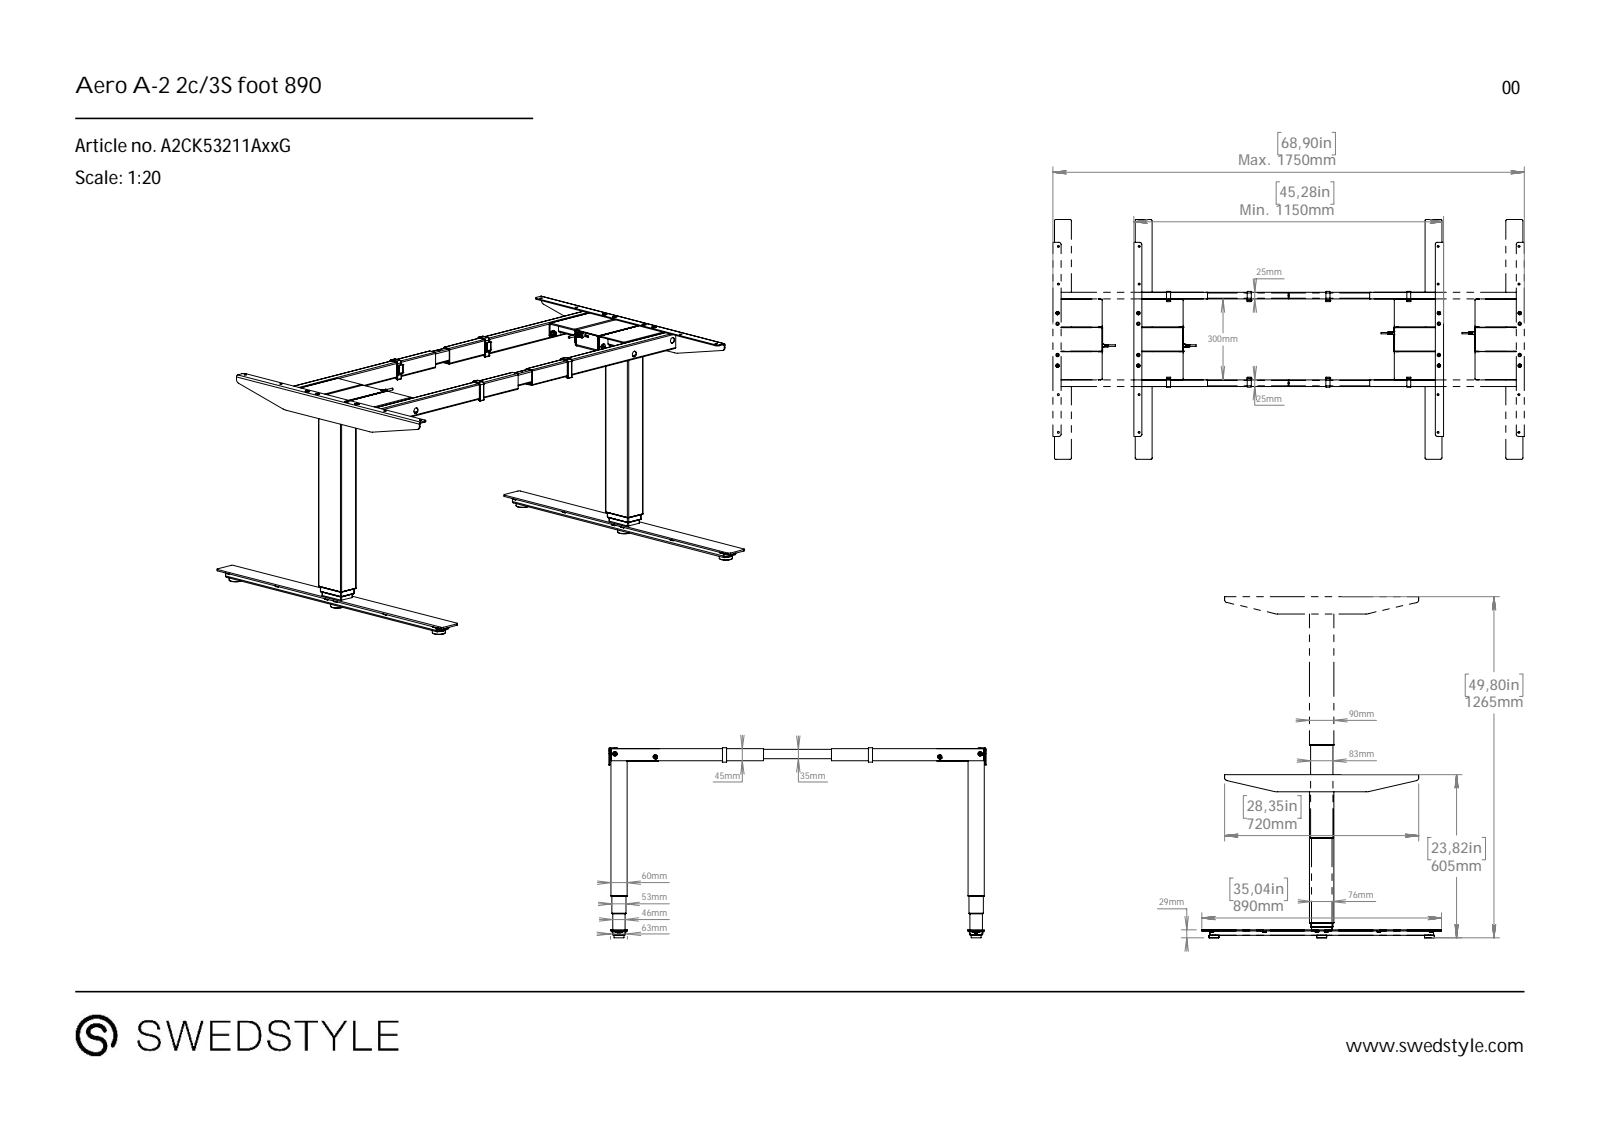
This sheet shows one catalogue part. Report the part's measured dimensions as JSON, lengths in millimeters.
{"part_name": "A2CK53211AxxG Aero A-2 2c_3S foot 890", "step_written_by": "SolidWorks 2021 (CONFIG_CONTROL_DESIGN)", "units": "millimeters", "bodies": {"solids": 0, "faces": 1205, "planar": 528, "cylindrical": 393, "other": 284}, "overall_size": [1400, 890, 705], "round_holes": [[16, 12], [7, 8], [7.5, 4], [4.2, 2], [5.4, 2], [8, 2]], "round_bosses_or_shafts": [[15.57, 4], [6, 4], [8.5, 2], [8, 2], [5.5, 2]], "partial_cylinders_radius": [[2.5, 74], [0.5, 22], [3, 20], [5, 18], [2.8, 16], [2.3, 8], [3.5, 8], [1, 6]], "face_to_face_distances": [2, 3.5, 2.5, 3, 1326, 0.5, 6.9, 3.4, 325, 4], "hole_center_spacings": [22, 34, 40.5, 41.98, 51.4, 75.54, 81.15, 110.32]}
